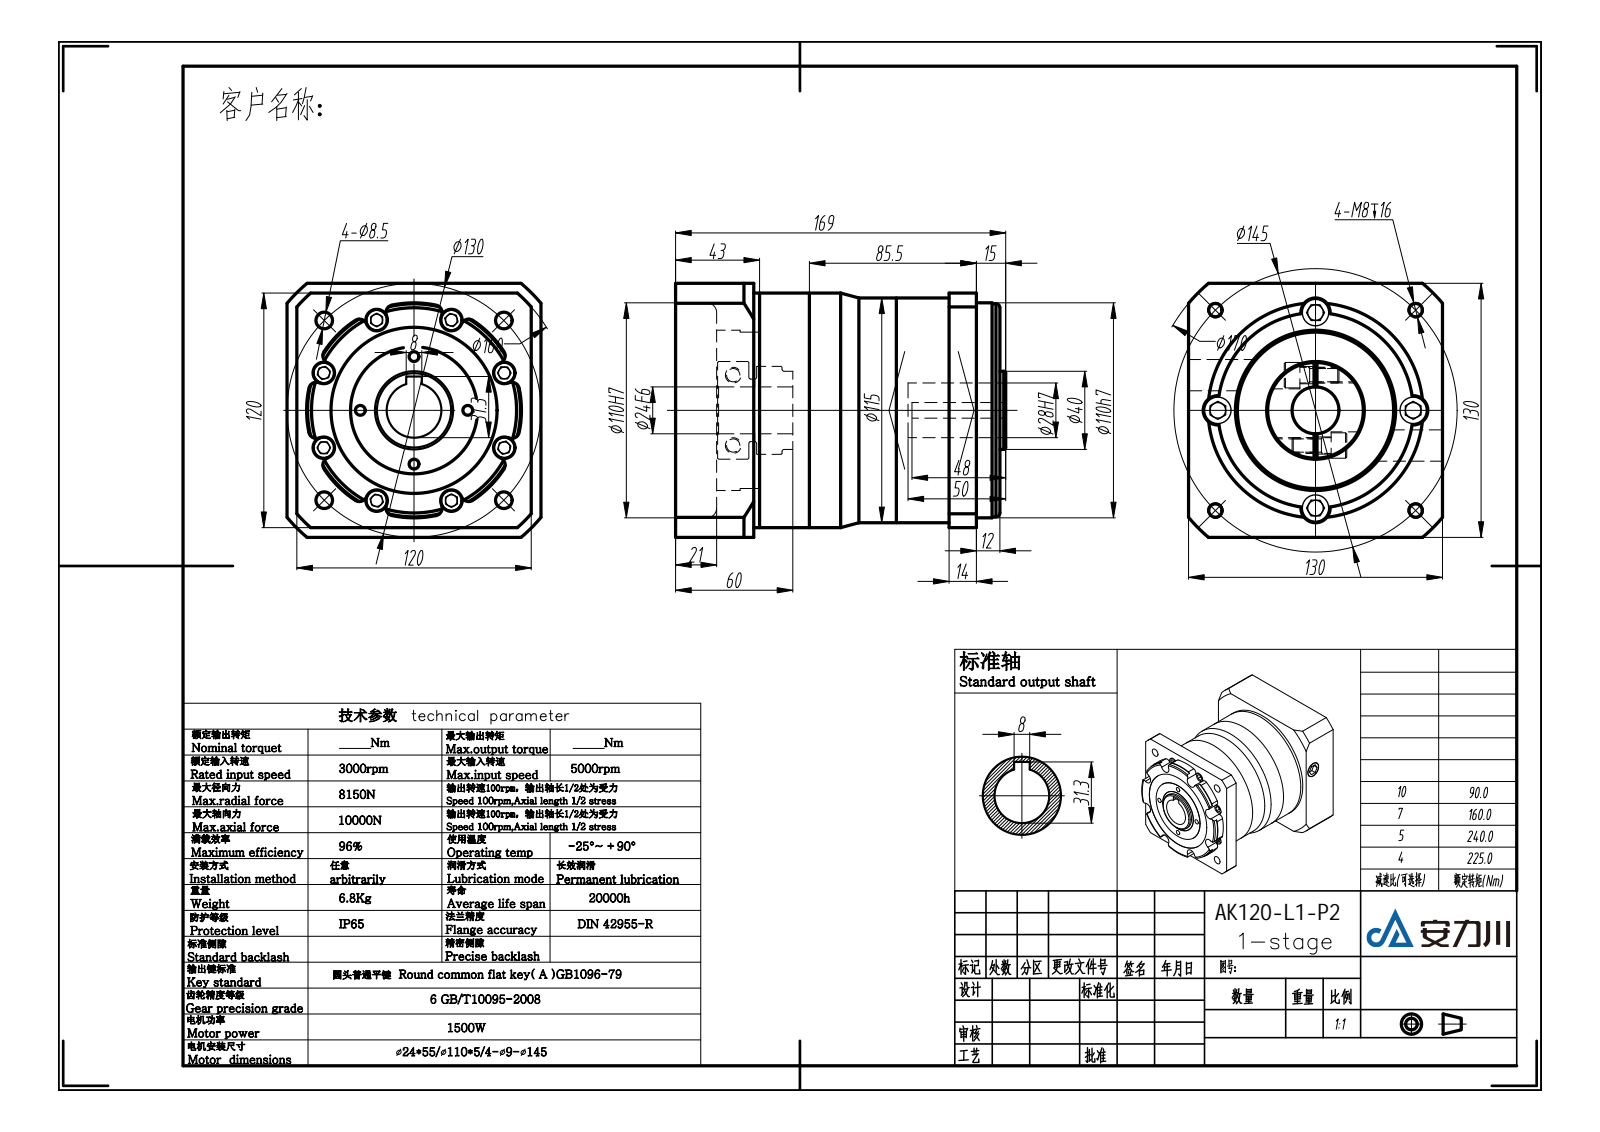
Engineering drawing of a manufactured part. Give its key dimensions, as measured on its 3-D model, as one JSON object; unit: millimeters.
{"part_name": "VGK115单级模型（24-55 110-5 4-9-145）", "step_written_by": "SolidWorks 2016 (AUTOMOTIVE_DESIGN)", "units": "millimeters", "bodies": {"solids": 4, "faces": 372, "planar": 176, "cylindrical": 167, "other": 29}, "overall_size": [169, 130, 130], "volume_mm3": 1726000, "surface_area_mm2": 212167, "round_holes": [[11, 8], [5, 4], [6.8, 4], [8.5, 4], [16, 2], [24, 1], [28, 1], [45.2, 1], [80, 1], [82, 1], [85, 1]], "round_bosses_or_shafts": [[9.5, 8], [13.5, 4], [15.6, 2], [120, 1], [115, 1], [110, 1], [65, 1], [50, 1]], "partial_cylinders_radius": [[4, 16], [7.5, 4], [54.5, 1], [80, 1], [85, 1]], "face_to_face_distances": [25.5, 70, 44.5, 97.5, 130, 26, 113, 5, 43, 68.5], "hole_center_spacings": [26.74, 26.83, 32.54, 46.94, 49.53, 49.99, 56.51, 65.09]}
